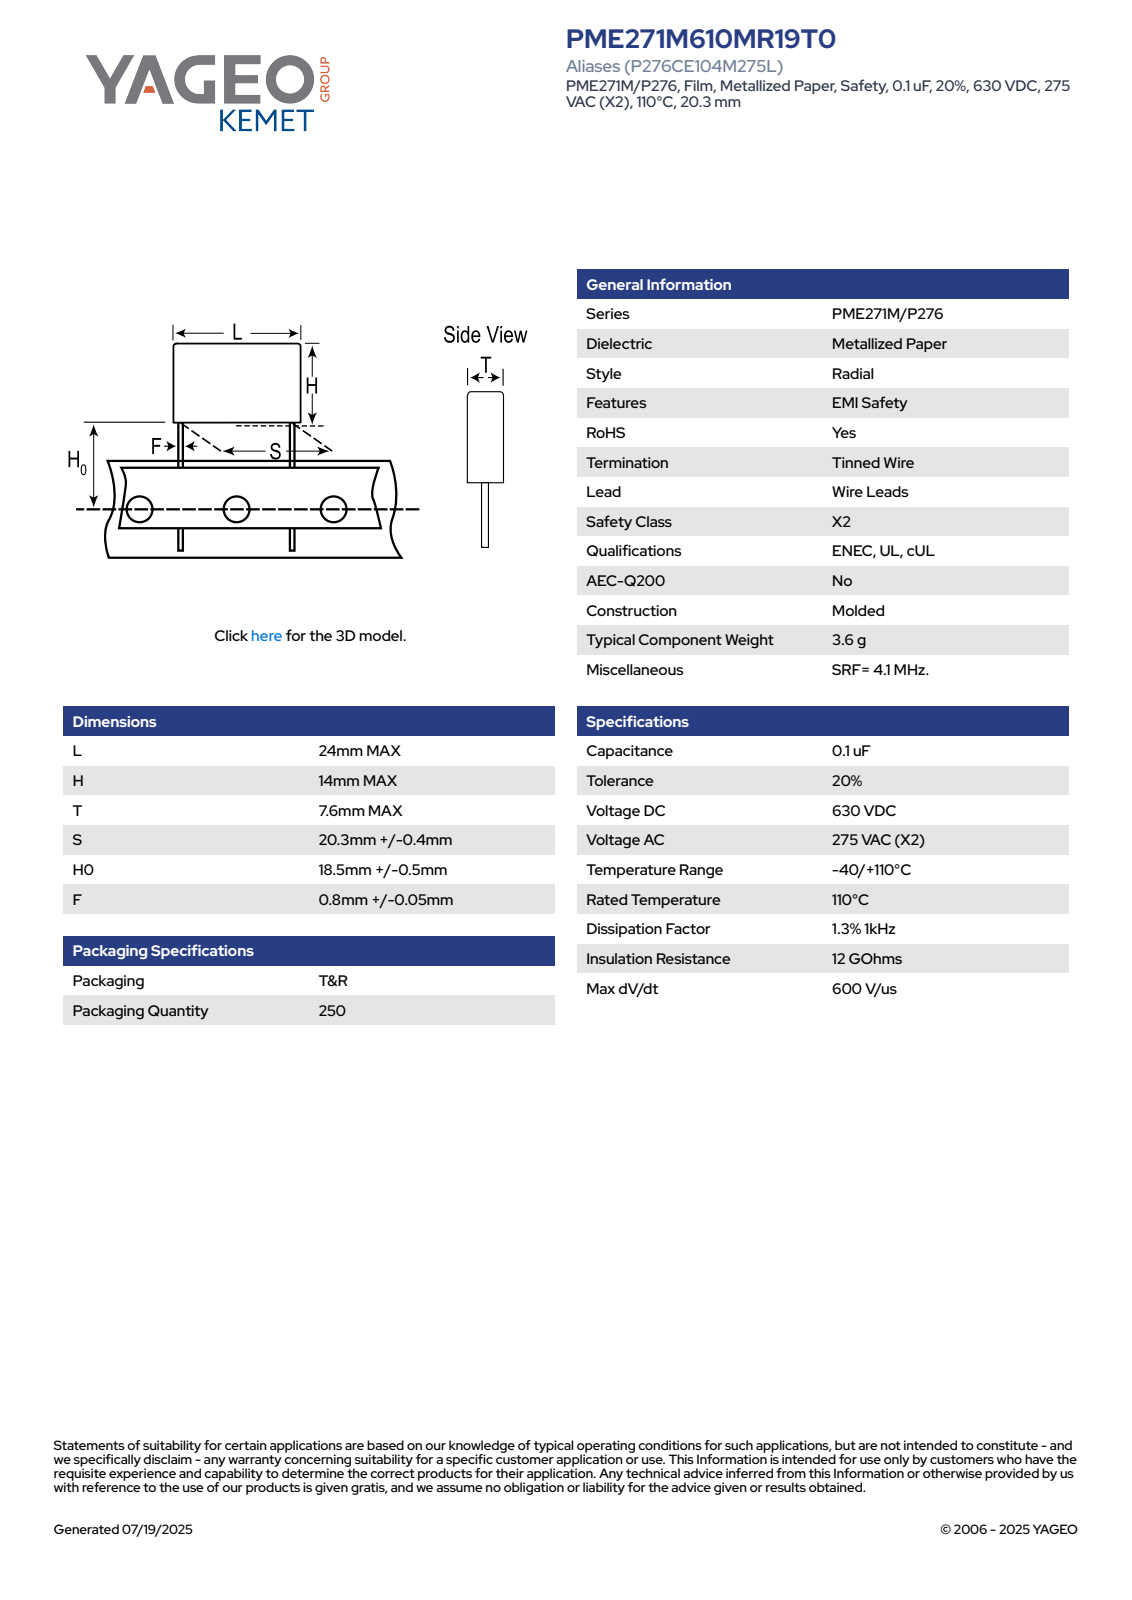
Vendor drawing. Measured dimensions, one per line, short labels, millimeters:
name: CFR_MOLDED_24X14X7.6_L24H14T7.6S20.3H019F0.85
written by: SolidWorks 2014 (AUTOMOTIVE_DESIGN)
unit: mm
bodies: 4 solids, 73 faces (65 planar, 8 cylindrical, 0 other)
size: 33 × 24 × 7.61
volume: 2 572 mm³; area: 1 365 mm²
bosses: 2× ⌀0.85
rounds: 4× R0.5
face distances: 7.6, 14, 24, 19, 33, 5.87, 27.02, 8.02, 5.98, 24.87
